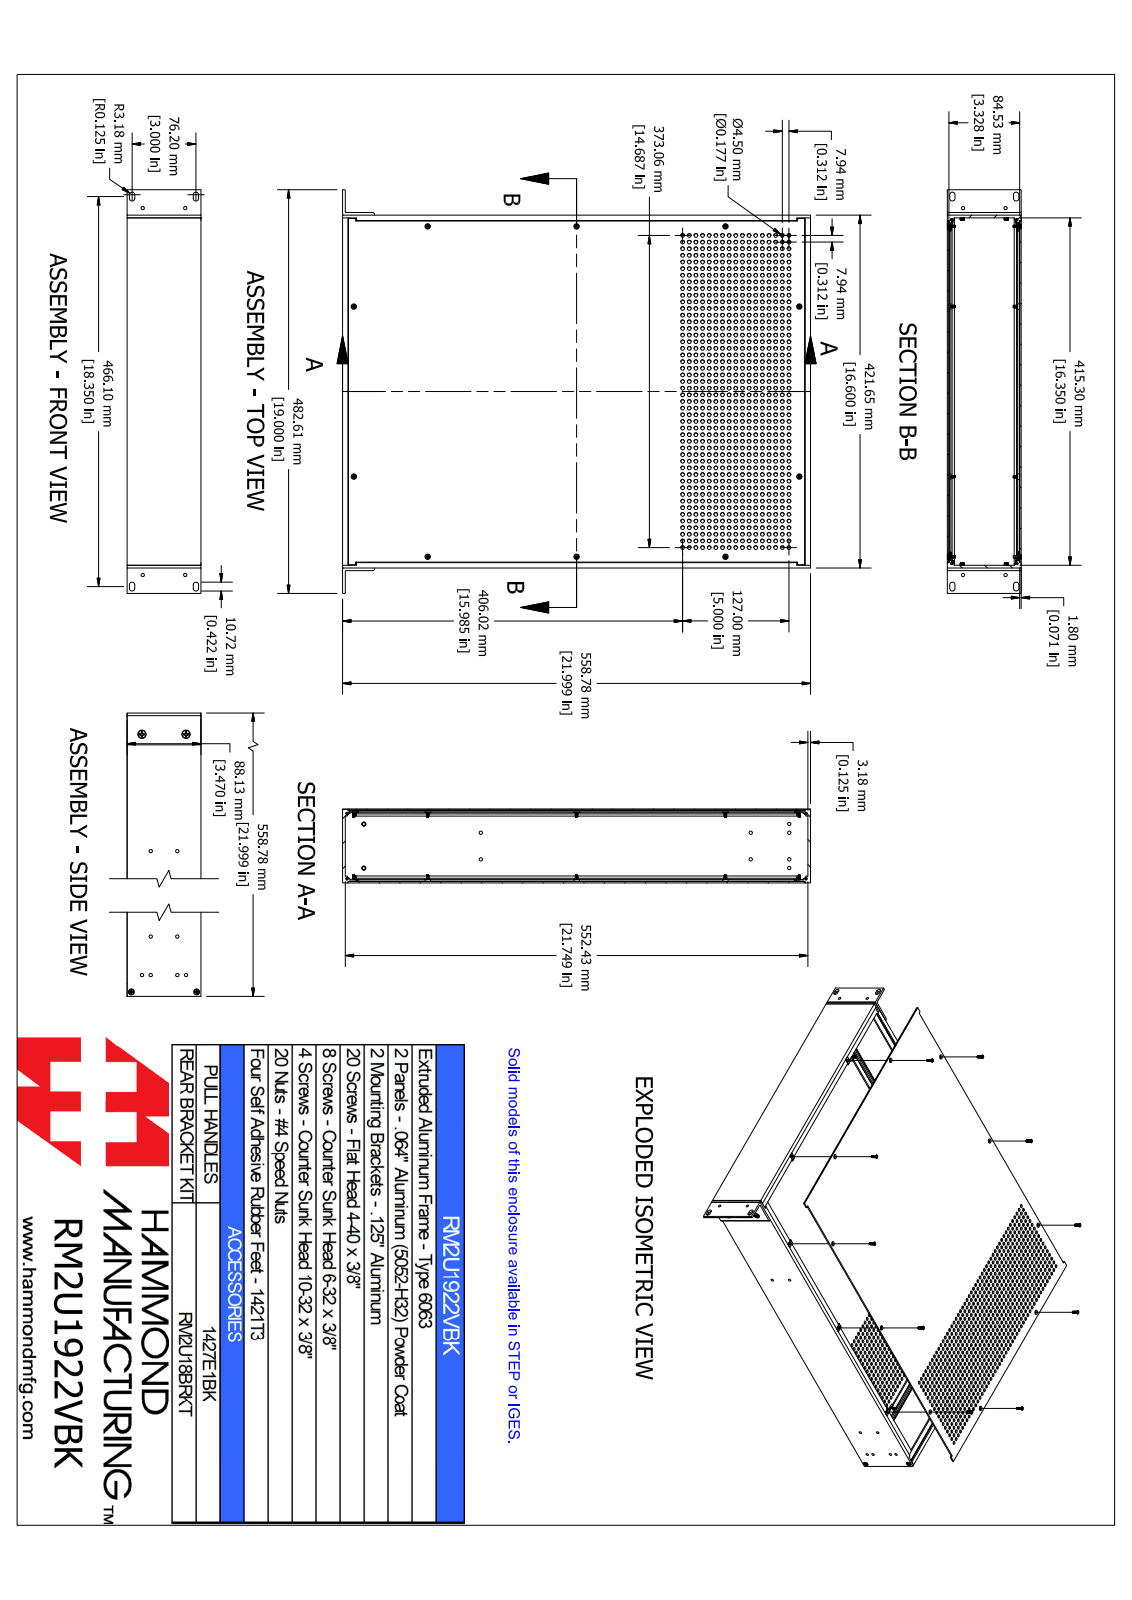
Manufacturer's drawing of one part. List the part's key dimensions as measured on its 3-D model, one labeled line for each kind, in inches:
Part name (STEP PRODUCT): RM2U1922VBK
STEP written by: SolidWorks 2021 (AUTOMOTIVE_DESIGN)
Units: inches
Bodies: 60 solids, 3916 faces (952 planar, 2176 cylindrical, 788 other)
Overall size (bounding box): 21.999 × 19 × 3.471
Volume: 91.29 in³ · Surface area: 2 165 in²
Round holes (diameter × count): ⌀0.177 ×1632, ⌀0.157 ×10, ⌀0.16 ×10, ⌀0.159 ×6, ⌀0.165 ×6, ⌀0.138 ×4, ⌀0.156 ×4, ⌀0.157 ×4, ⌀0.169 ×4, ⌀0.197 ×2
Round bosses / shafts (diameter × count): ⌀0.2 ×10, ⌀0.112 ×10, ⌀0.238 ×4, ⌀0.138 ×4, ⌀0.36 ×2, ⌀0.19 ×2
Partial cylindrical surfaces — rounded edges, fillets, slot ends (radius × count): R0.01 ×80, R0.024 ×80, R0.009 ×40, R0.014 ×40, R0.015 ×16, R0.038 ×16, R0.039 ×14, R0.035 ×8
Main face-to-face distances: 0.071, 3.399, 3.47, 3.328, 16.476, 0.125, 0.125, 21.874, 16.601, 16.35
Hole centre spacings: 7, 5.127, 17.049, 1.25, 8, 11.131, 12.274, 14
